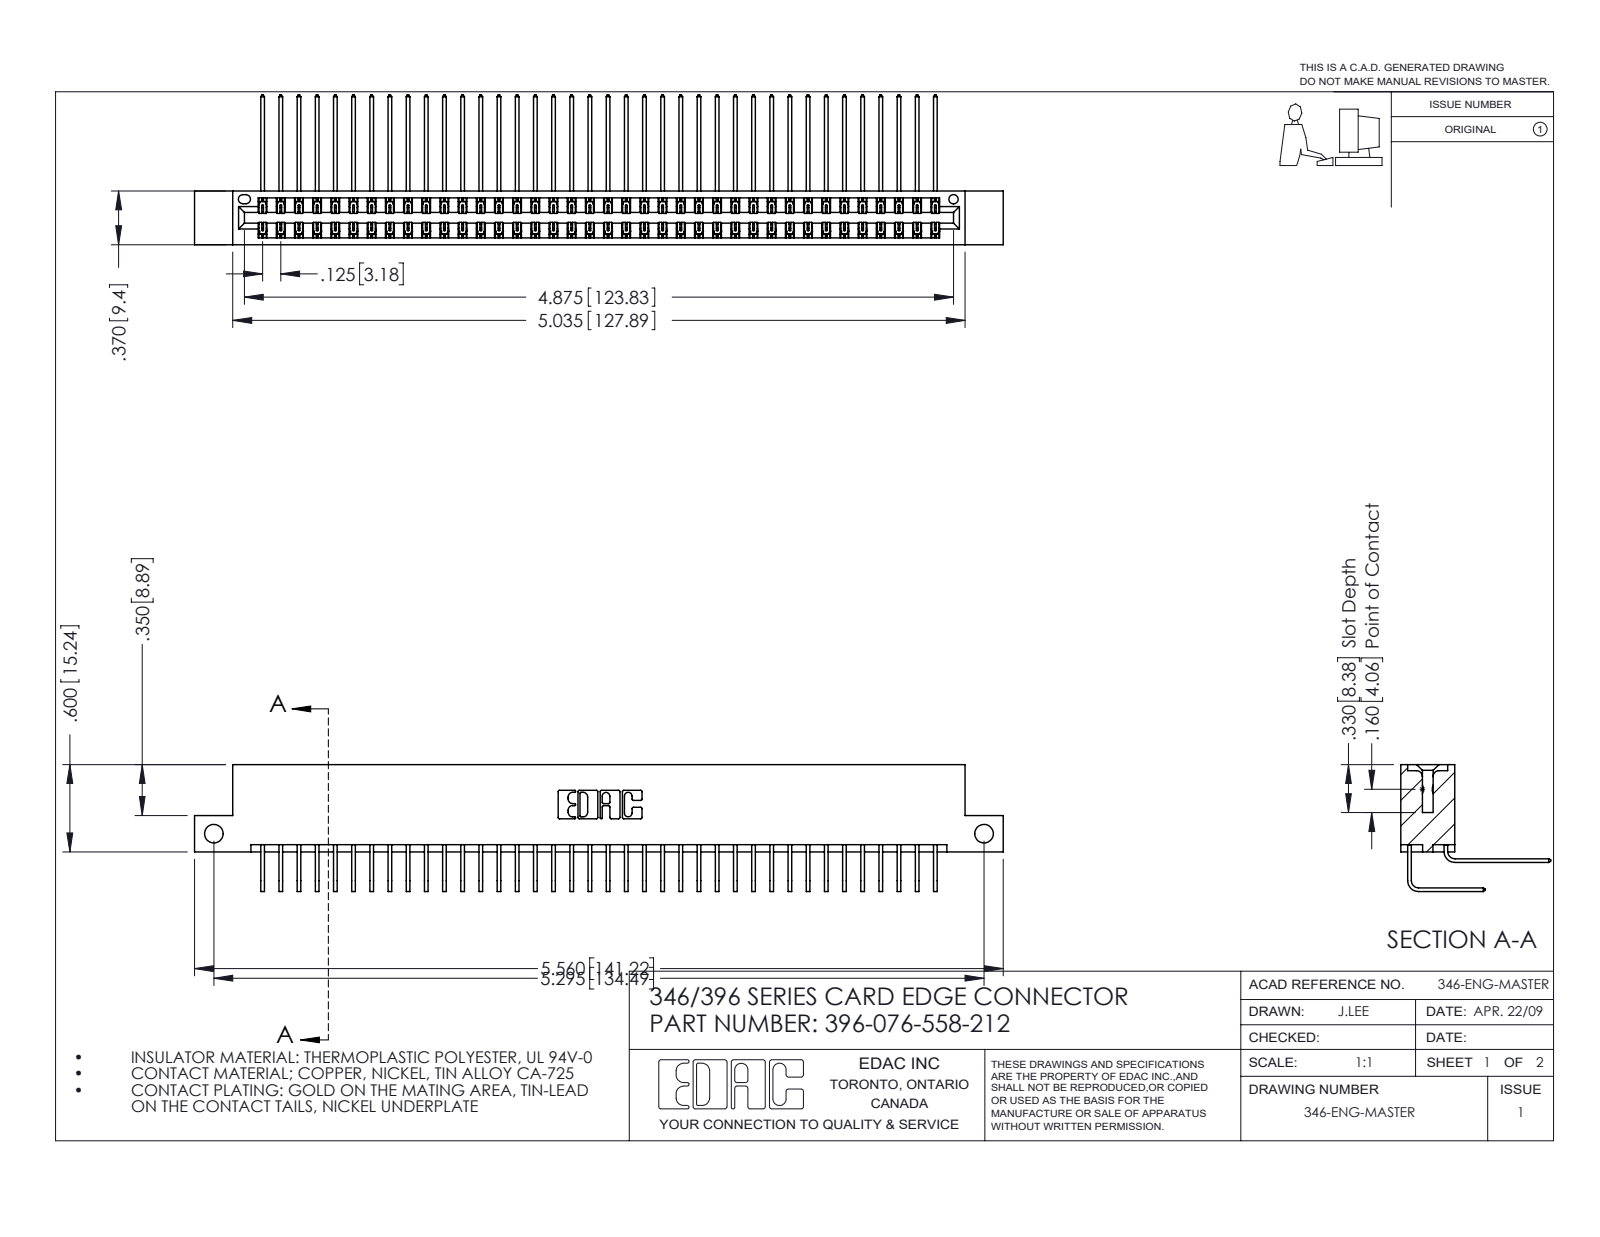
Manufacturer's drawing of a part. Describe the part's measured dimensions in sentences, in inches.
The part is named "345-292-001_558 Tail - 2; 396-076-558-212; 346 Part_Flush Mounting Lugs - Side Mount; 345-292-001_558 559 Tail - 1". Its 3-D file was written by "SolidWorks 2016 (CONFIG_CONTROL_DESIGN)". It is 77 solids with 4226 faces: 2888 planar, 1338 cylindrical and 0 other. Overall it measures 5.56 by 1.03 by 0.873 inches. Its volume is 0.86 cubic inches and its surface area 32.97 square inches. Round holes: 2 of diameter 0.128, 1 of diameter 0.064. Partial cylindrical surfaces (rounded edges, fillets, slot ends): 114 of radius 0.006, 22 of radius 0.01, 6 of radius 0.007, 6 of radius 0.031, 3 of radius 0.026, 2 of radius 0.014, 2 of radius 0.022, 2 of radius 0.024. The main face-to-face distances are 0.322, 0.048, 0.025, 0.25, 0.37, 0.298, 0.072, 0.275, 0.148, 0.222. The hole center spacings are 5.295.
